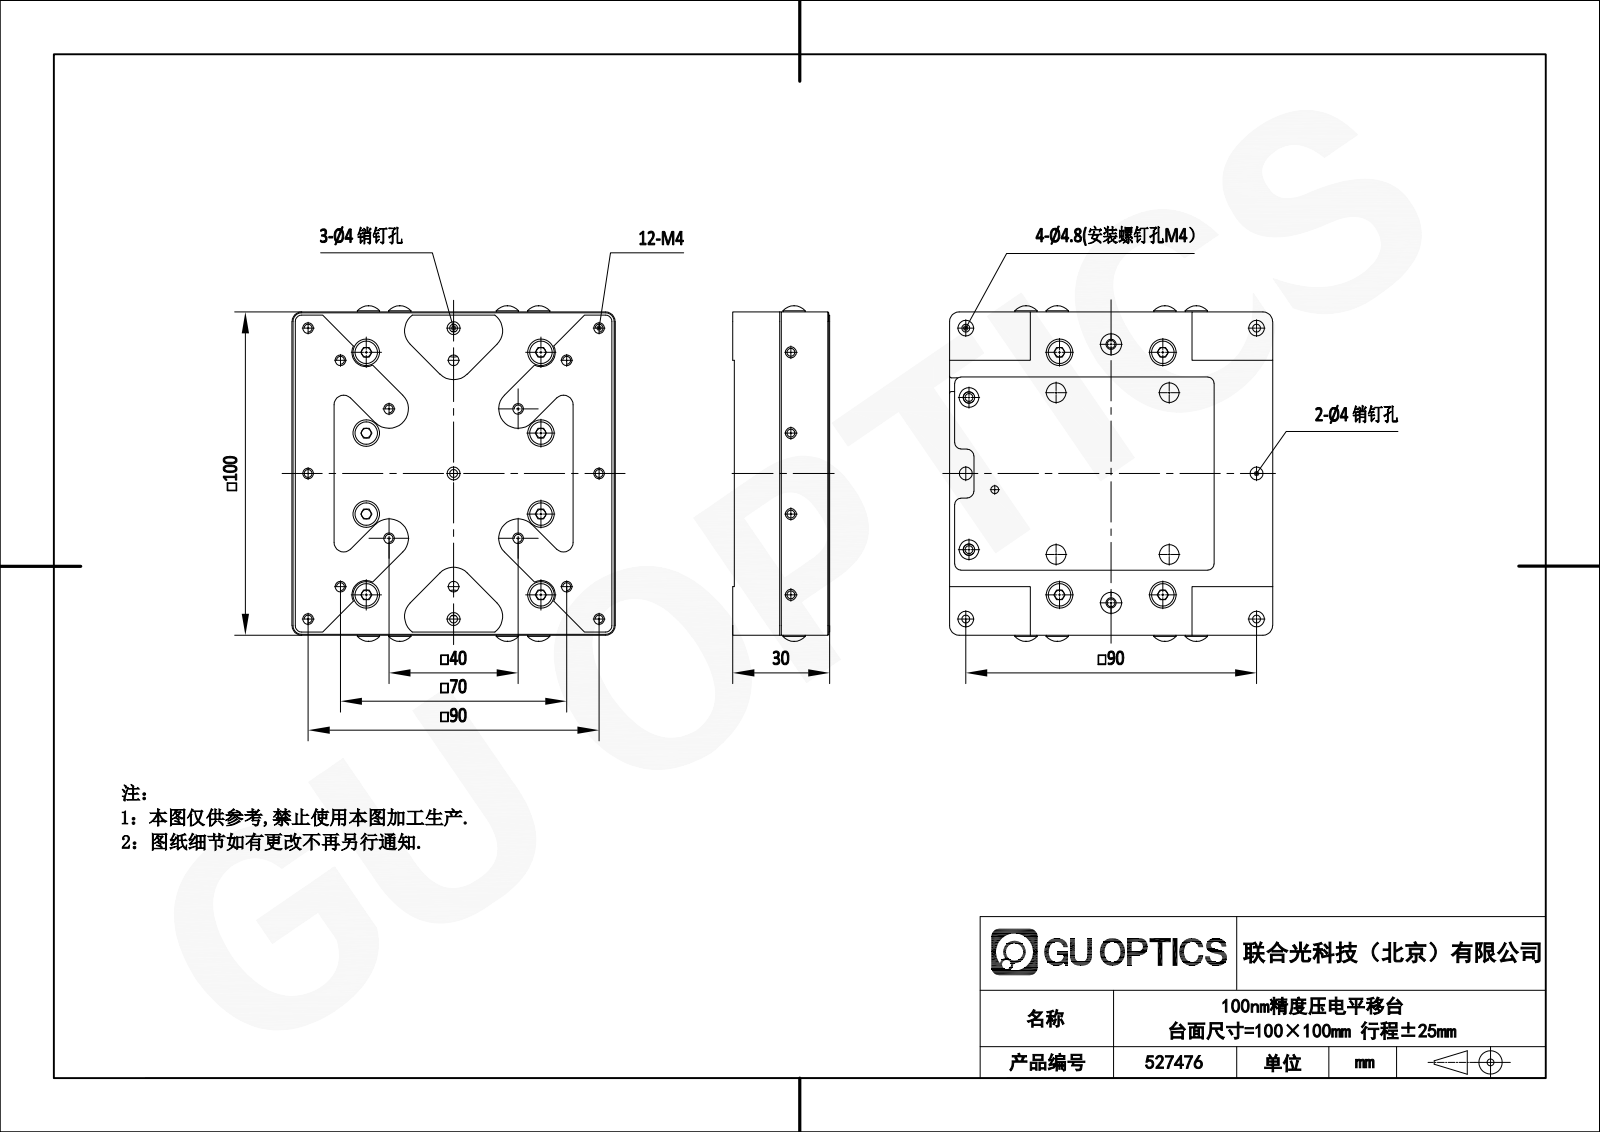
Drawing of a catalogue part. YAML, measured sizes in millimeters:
part_name: "527476"
step_written_by: "SolidWorks 2020 (CONFIG_CONTROL_DESIGN)"
units: millimeters
bodies: {solids: 25, faces: 1412, planar: 644, cylindrical: 556, other: 212}
overall_size: [103.8, 100, 30]
volume: 291429
surface_area: 99058
round_holes:
  - {diameter: 2.5, count: 22}
  - {diameter: 4.5, count: 18}
  - {diameter: 3.3, count: 16}
  - {diameter: 3.4, count: 16}
  - {diameter: 6, count: 16}
  - {diameter: 8.25, count: 16}
  - {diameter: 3.6, count: 6}
  - {diameter: 6.2, count: 6}
  - {diameter: 4, count: 5}
  - {diameter: 3.5, count: 4}
  - {diameter: 4.8, count: 4}
  - {diameter: 2.6, count: 2}
round_bosses_or_shafts:
  - {diameter: 3, count: 28}
  - {diameter: 7, count: 12}
  - {diameter: 4, count: 12}
  - {diameter: 6.9, count: 4}
  - {diameter: 5.5, count: 2}
partial_cylinders:
  - {radius: 2.5, count: 34}
  - {radius: 3, count: 19}
  - {radius: 2, count: 14}
  - {radius: 6, count: 10}
  - {radius: 1.9, count: 6}
  - {radius: 0.8, count: 4}
  - {radius: 1, count: 4}
  - {radius: 1.48, count: 4}
face_to_face_distances: [0.5, 8.5, 9, 14.5, 6.2, 23, 29.2, 15, 8.3, 14]
hole_center_spacings: [25, 27.31, 49.74, 50, 11, 43, 51.2, 65.95]
